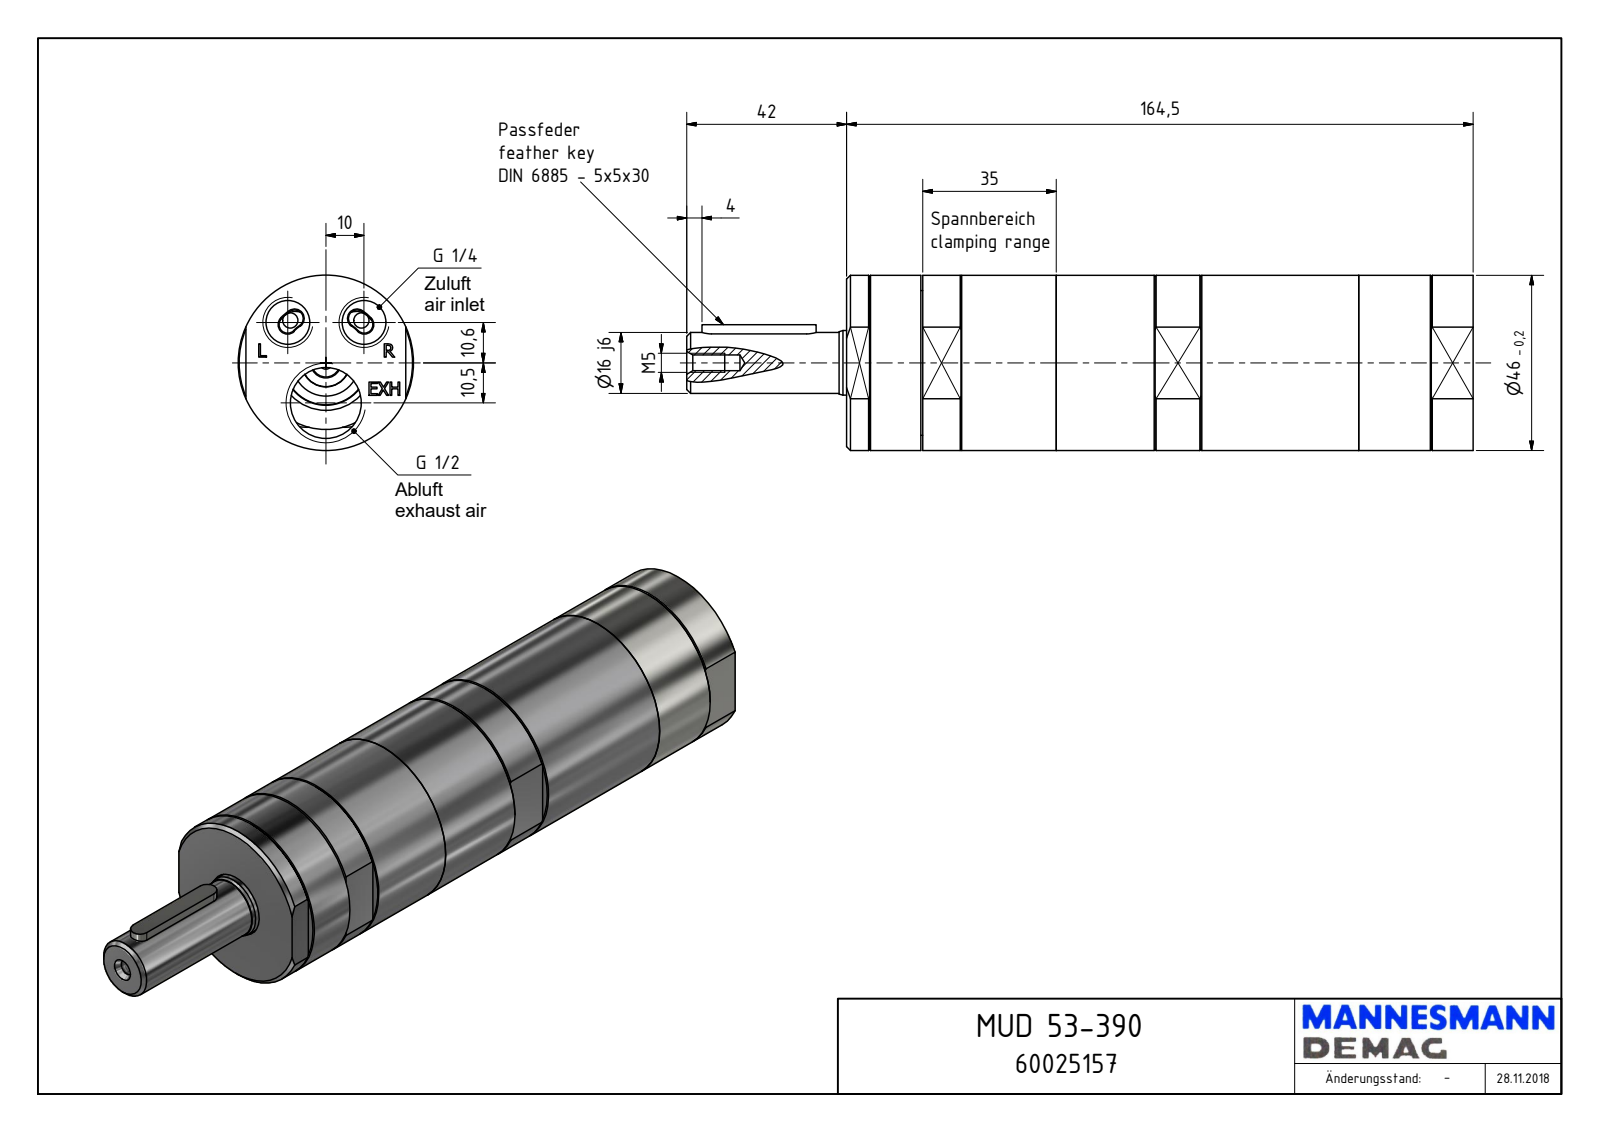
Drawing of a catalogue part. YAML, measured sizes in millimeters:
part_name: "MUD 53-390_60025157"
step_written_by: "Autodesk Inventor 2018 (AUTOMOTIVE_DESIGN)"
units: millimeters
bodies: {solids: 1, faces: 171, planar: 100, cylindrical: 34, other: 37}
overall_size: [206.5, 46, 46]
volume: 275188
surface_area: 33922
round_holes:
  - {diameter: 11.45, count: 2}
  - {diameter: 4.13, count: 1}
  - {diameter: 17.5, count: 1}
  - {diameter: 18.63, count: 1}
  - {diameter: 21.5, count: 1}
  - {diameter: 23, count: 1}
  - {diameter: 38, count: 1}
  - {diameter: 38.38, count: 1}
round_bosses_or_shafts:
  - {diameter: 46, count: 1}
  - {diameter: 33.71, count: 1}
  - {diameter: 19.56, count: 1}
  - {diameter: 16.95, count: 1}
  - {diameter: 16, count: 1}
partial_cylinders:
  - {radius: 2.5, count: 2}
  - {radius: 5, count: 2}
face_to_face_distances: [164.5, 42, 6.34, 20, 144.5, 19.5, 0.5, 145, 158.16, 138.66]
hole_center_spacings: [14.57, 23.35, 10.5, 20]
